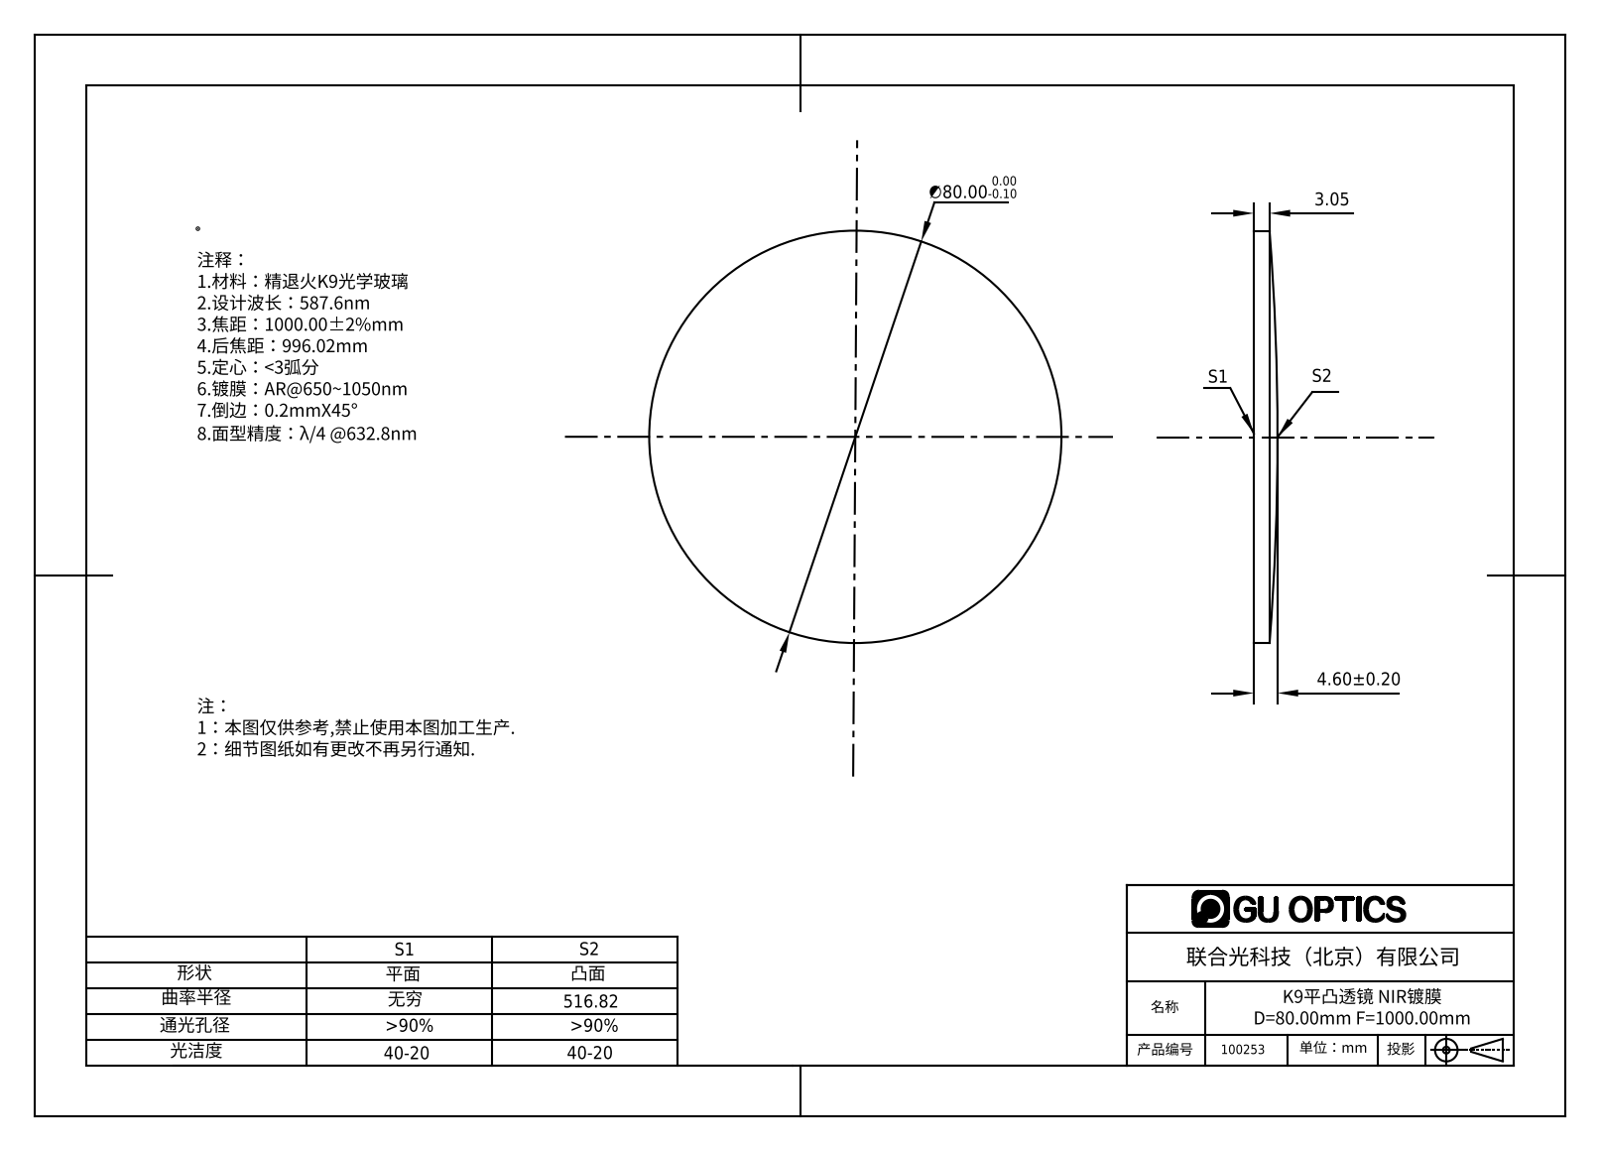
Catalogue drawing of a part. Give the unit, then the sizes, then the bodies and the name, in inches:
Units: inches
Overall size (bounding box): 3.15 × 3.15 × 0.181
Round bosses / shafts (diameter × count): ⌀3.15 ×1
Volume: 1.173 in³ · Surface area: 16.78 in²
Bodies: 1 solid, 5 faces (1 planar, 2 cylindrical, 2 other)
Part name (STEP PRODUCT): 100081
STEP written by: SolidWorks 2016 (AUTOMOTIVE_DESIGN)
